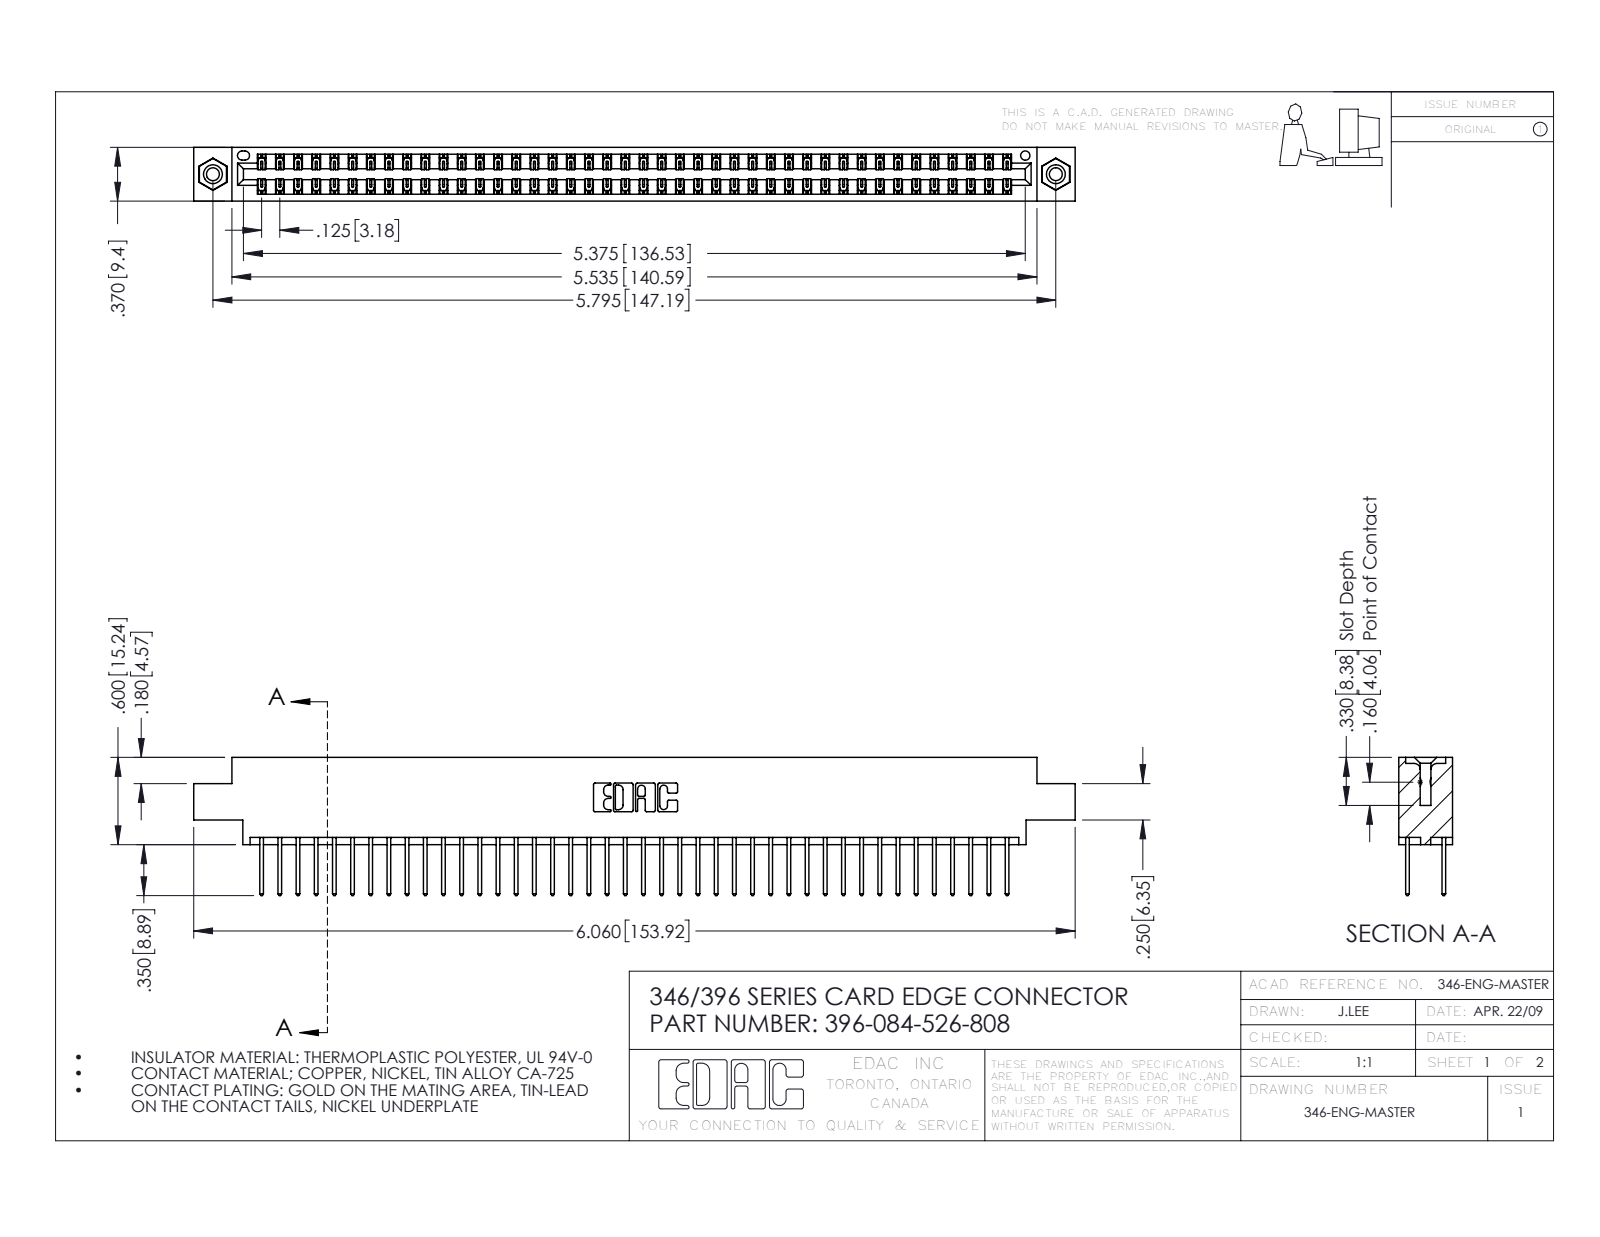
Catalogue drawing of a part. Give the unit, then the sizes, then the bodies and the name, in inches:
Units: inches
Overall size (bounding box): 6.06 × 0.95 × 0.37
Round holes (diameter × count): ⌀0.089 ×2, ⌀0.125 ×2, ⌀0.156 ×2, ⌀0.064 ×1
Round bosses / shafts (diameter × count): ⌀0.155 ×2
Partial cylindrical surfaces — rounded edges, fillets, slot ends (radius × count): R0.006 ×126, R0.01 ×84, R0.01 ×22, R0.007 ×6, R0.031 ×6, R0.026 ×3, R0.014 ×2, R0.022 ×2
Main face-to-face distances: 0.048, 0.322, 0.25, 0.37, 0.072, 0.298, 0.025, 0.275, 0.222, 0.148
Hole centre spacings: 0.246, 5.586, 5.795
Volume: 0.915 in³ · Surface area: 33.19 in²
Bodies: 87 solids, 4554 faces (3052 planar, 1486 cylindrical, 16 other)
Part name (STEP PRODUCT): 396-084-526-808; 345-292-001_345-293-126; 345-250-001_345-250-003-102; 346 Part_0.170 Offset - 0.156 Dia-TI
STEP written by: SolidWorks 2016 (CONFIG_CONTROL_DESIGN)
